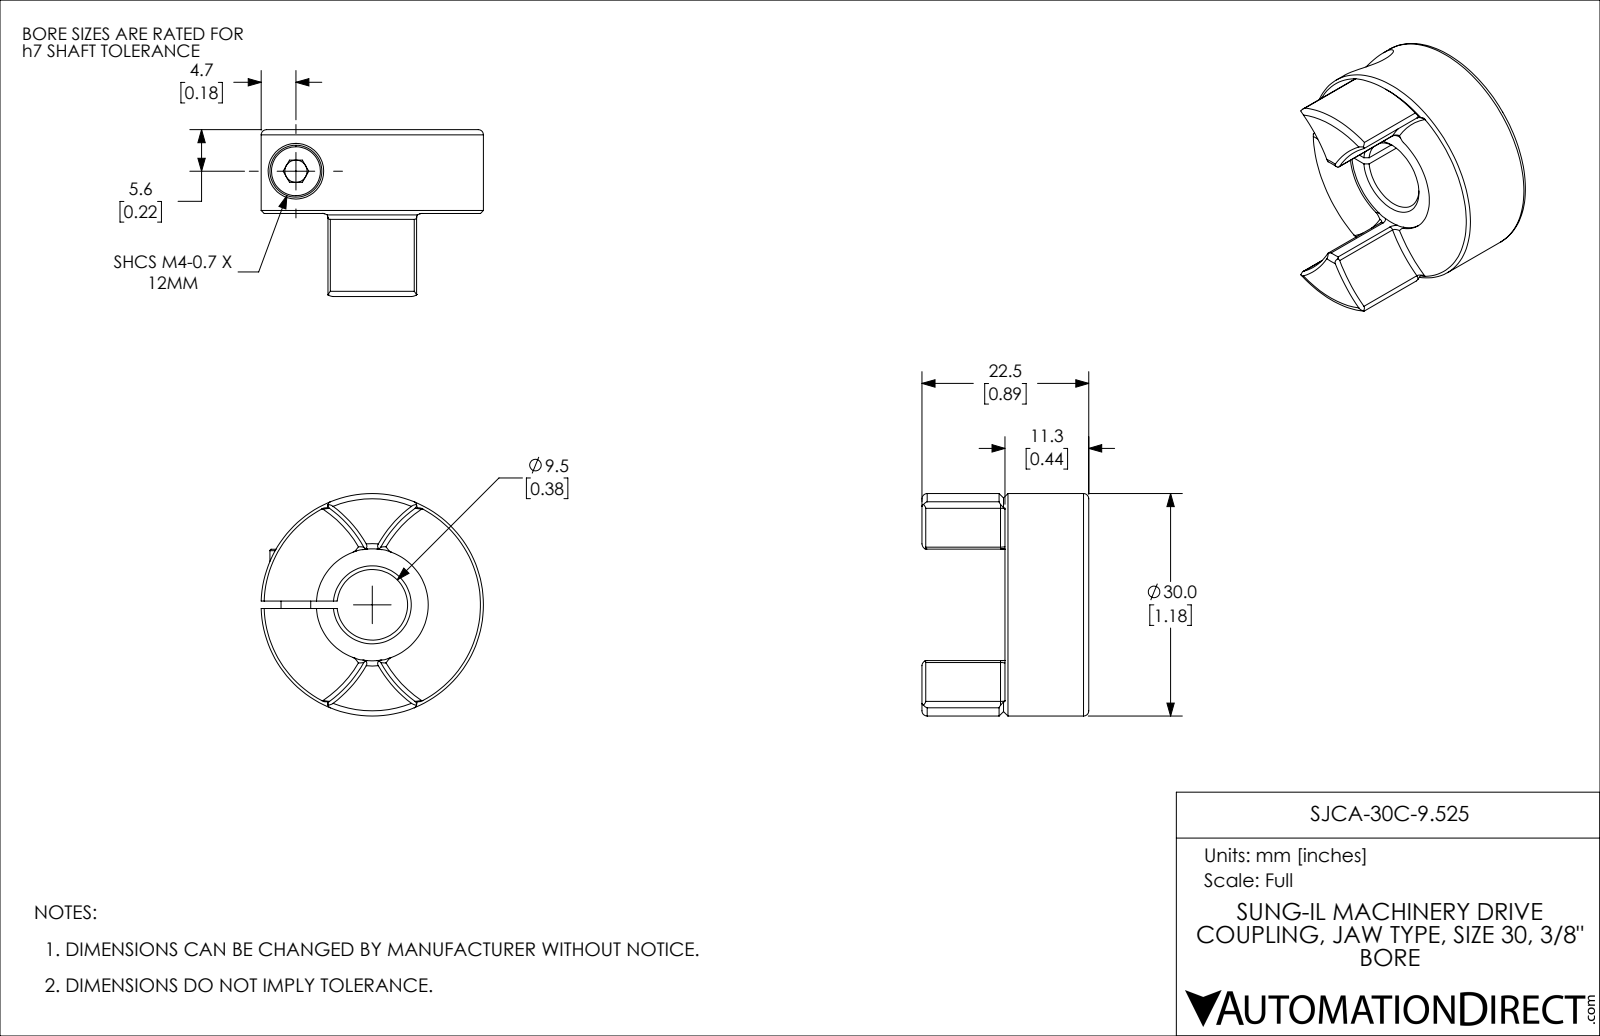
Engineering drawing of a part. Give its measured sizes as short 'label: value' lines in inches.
name: SJCA-30C-9.525
written by: SolidWorks 2021 (CONFIG_CONTROL_DESIGN)
unit: in
bodies: 2 solids, 109 faces (27 planar, 41 cylindrical, 41 other)
size: 1.181 × 1.181 × 0.886
volume: 0.486 in³; area: 6.36 in²
holes: 1× ⌀0.118, 1× ⌀0.13, 1× ⌀0.173, 1× ⌀0.295, 1× ⌀0.375, 1× ⌀0.594
bosses: 1× ⌀1.181, 1× ⌀0.276, 1× ⌀0.157
rounds: 8× R0.02, 2× R0.634, 1× R1.083
face distances: 0.445, 0.039, 0.433, 0.157, 0.441, 0.453, 0.886, 0.118, 0.315, 0.276
